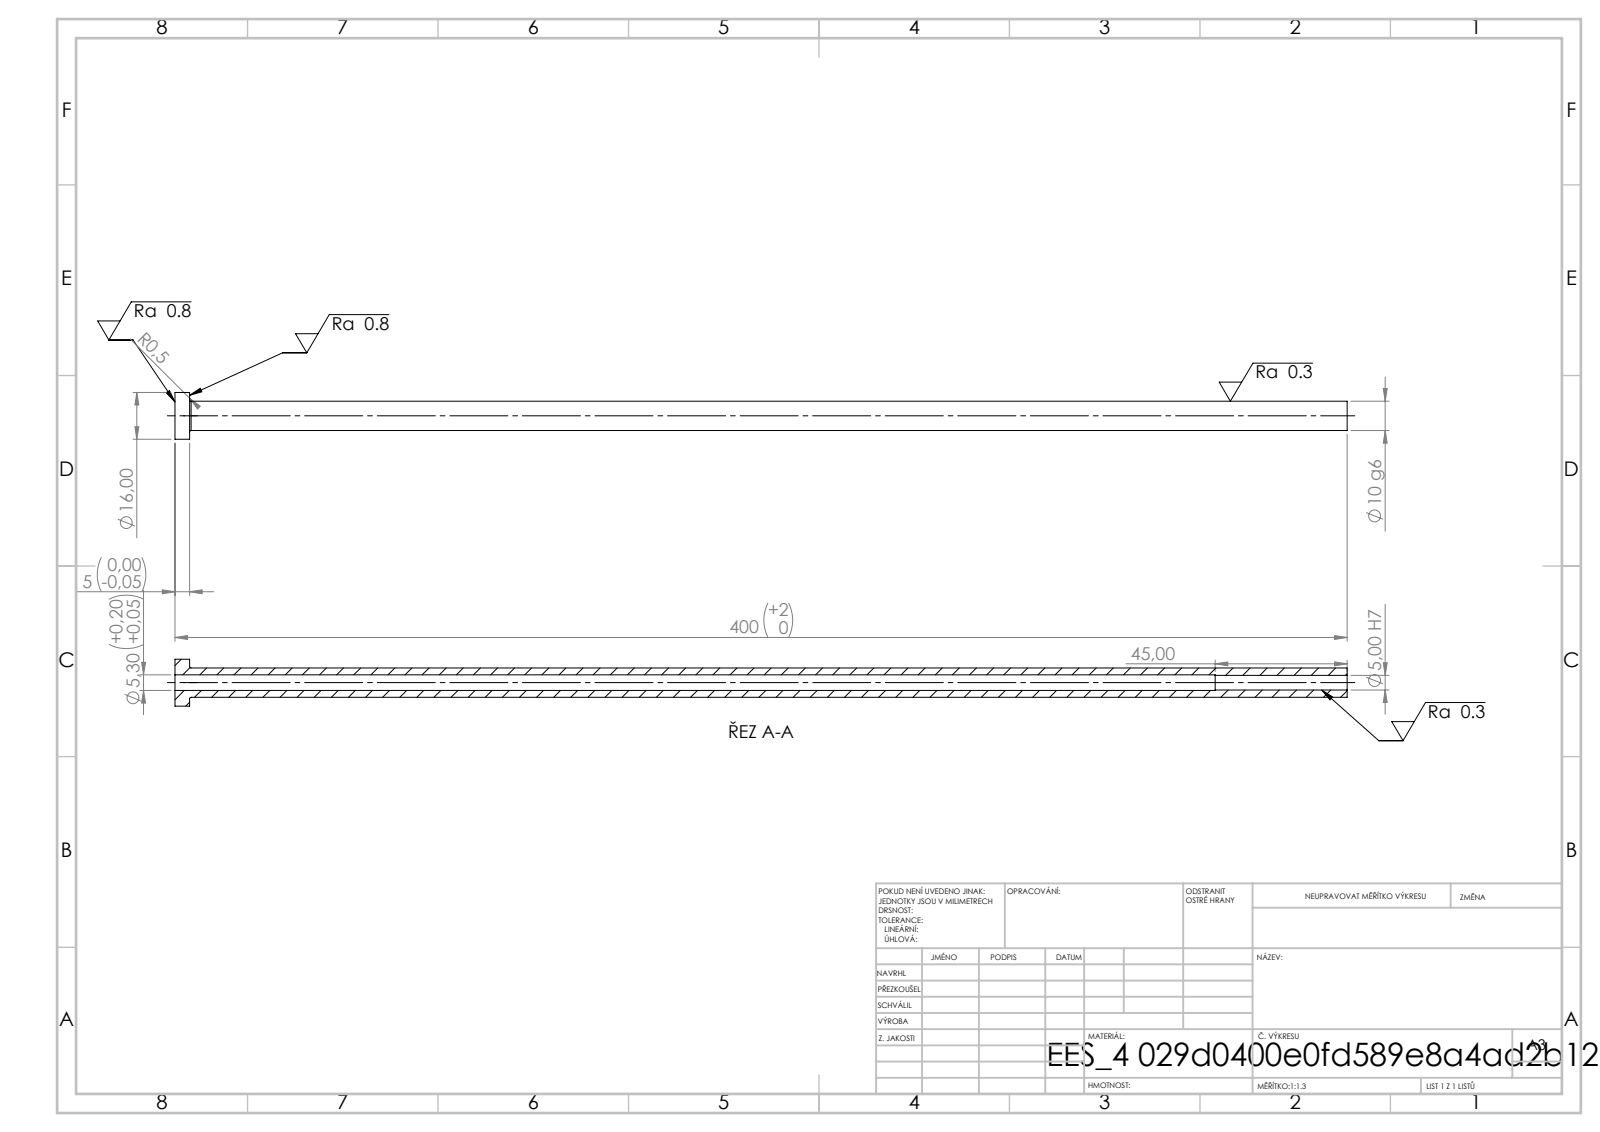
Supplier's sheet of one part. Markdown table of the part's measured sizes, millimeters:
| quantity | value |
| --- | --- |
| STEP written by | SolidWorks 2019 (CONFIG_CONTROL_DESIGN) |
| units | millimeters |
| bodies | 1 solid, 14 faces (4 planar, 8 cylindrical, 2 other) |
| overall size | 400 × 16 × 16 |
| volume | 23 315 mm³ |
| surface area | 19 635 mm² |
| round holes (diameter × count) | 5 × 1, 5.3 × 1 |
| round bosses / shafts (diameter × count) | 16 × 1, 10 × 1 |
| main face-to-face distances | 5, 400, 395, 355, 350, 45 |
